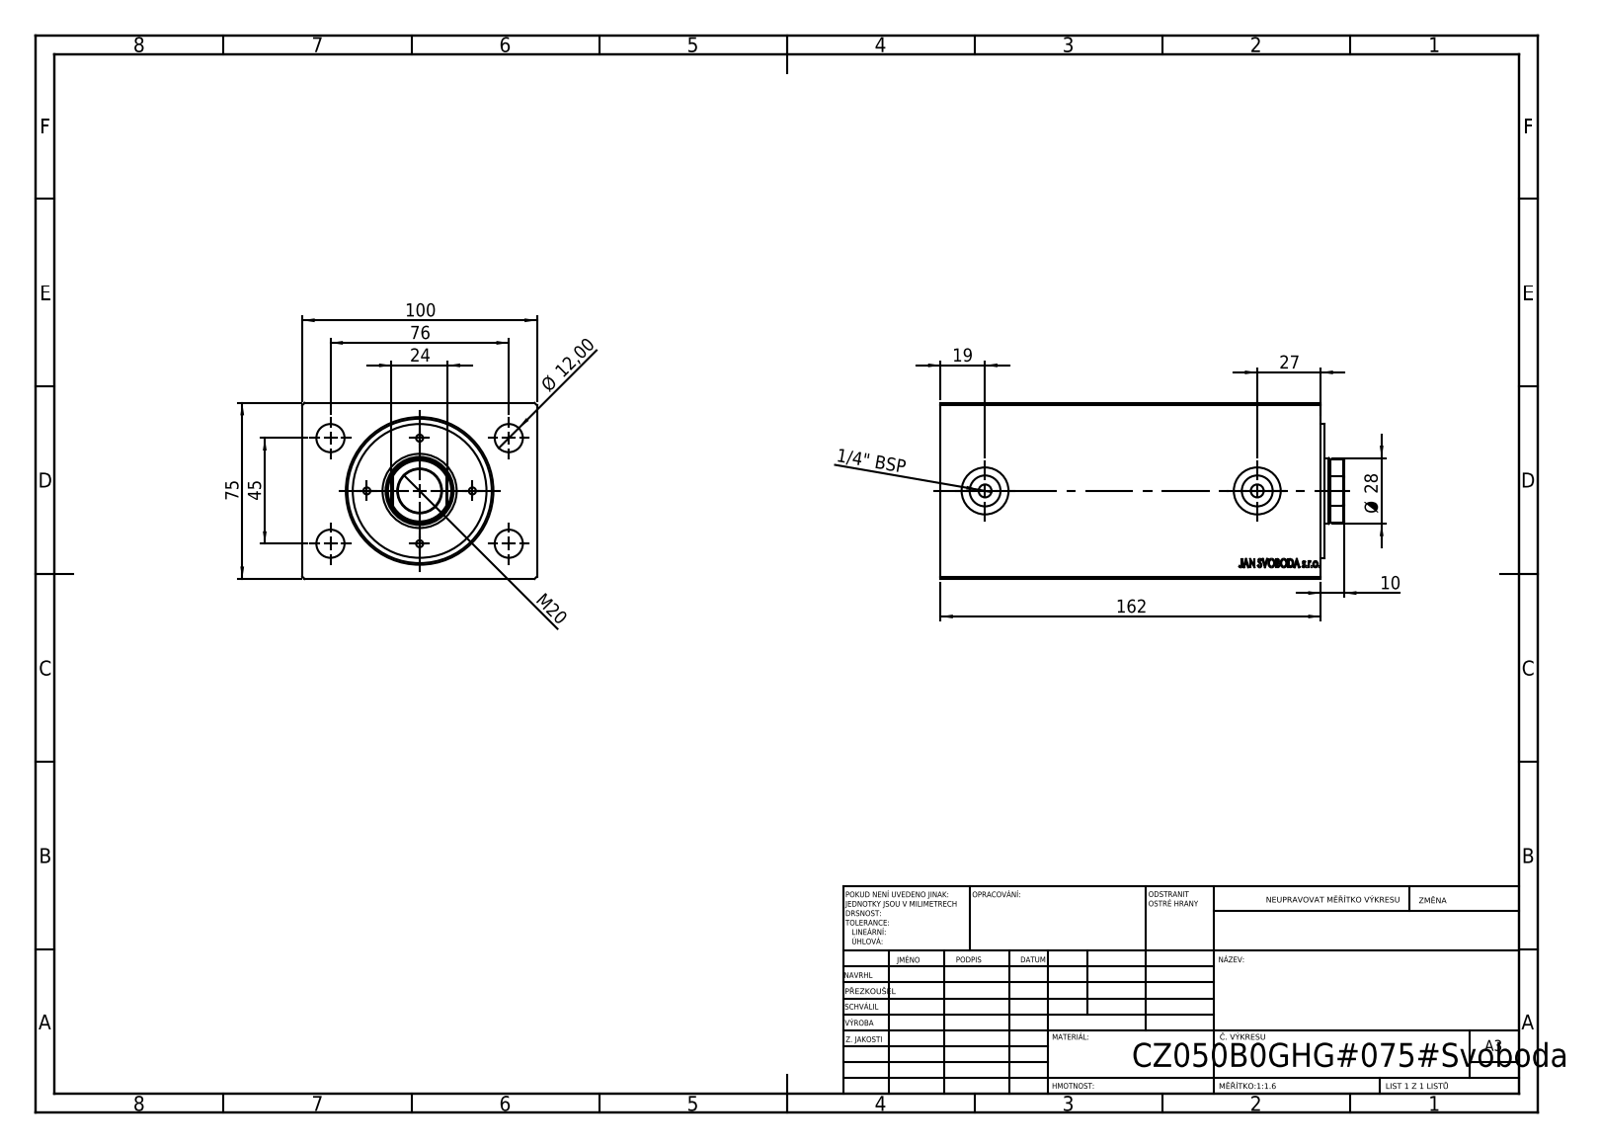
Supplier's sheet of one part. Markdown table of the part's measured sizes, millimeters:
| quantity | value |
| --- | --- |
| part name | V500CZ_B_VC; V500CZ |
| STEP written by | SolidWorks 2019 (CONFIG_CONTROL_DESIGN) |
| units | millimeters |
| bodies | 3 solids, 874 faces (400 planar, 58 cylindrical, 416 other) |
| overall size | 172 × 100 × 75 |
| volume | 1 082 000 mm³ |
| surface area | 133 961 mm² |
| round holes (diameter × count) | 3 × 4, 12 × 4, 5.5 × 2, 13.16 × 2, 20 × 2, 18.5 × 1, 28 × 1, 29 × 1, 36 × 1, 50 × 1, 61.5 × 1 |
| round bosses / shafts (diameter × count) | 57 × 1 |
| partial cylindrical surfaces (radius × count) | 13.5 × 1 |
| main face-to-face distances | 75, 100, 162, 144.2, 17.8, 10, 1.8, 8.2, 76.8, 136 |
| hole center spacings | 22.5, 27.32, 31.82, 38, 44.16, 45, 58.9, 64.55 |
